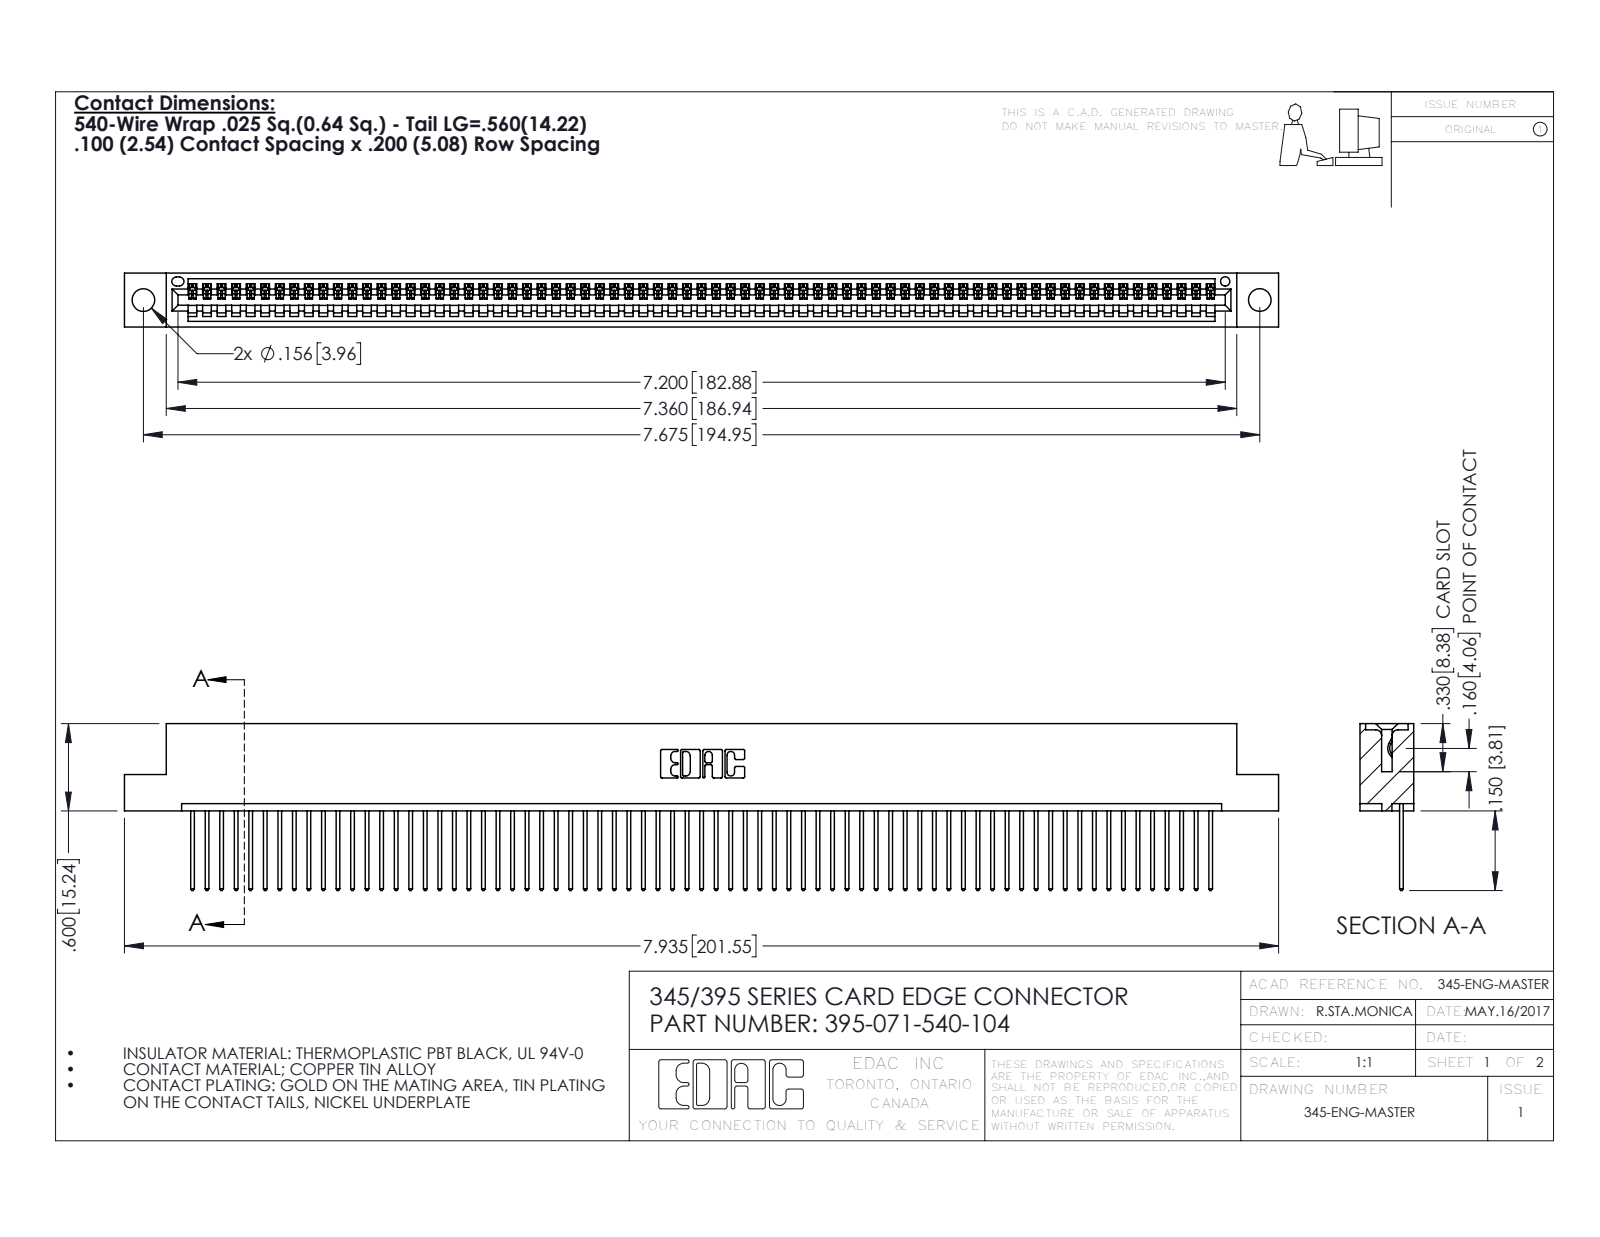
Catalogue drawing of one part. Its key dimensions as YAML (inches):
part_name: "345-292-001_345-293-140; 345 Part_Flush Mounting Lugs - 0.156 Dia-TH; 395-071-540-104"
step_written_by: "SolidWorks 2016 (CONFIG_CONTROL_DESIGN)"
units: inches
bodies: {solids: 72, faces: 4244, planar: 2920, cylindrical: 1324, other: 0}
overall_size: [7.935, 1.147, 0.37]
volume: 1.183
surface_area: 41.32
round_holes:
  - {diameter: 0.156, count: 2}
  - {diameter: 0.064, count: 1}
partial_cylinders:
  - {radius: 0.006, count: 142}
  - {radius: 0.01, count: 142}
  - {radius: 0.01, count: 22}
  - {radius: 0.007, count: 6}
  - {radius: 0.031, count: 6}
  - {radius: 0.026, count: 3}
  - {radius: 0.031, count: 2}
  - {radius: 0.04, count: 2}
face_to_face_distances: [0.072, 0.298, 0.37, 0.098, 0.272, 0.025, 0.2, 0.225, 0.149, 0.072]
hole_center_spacings: [0.27, 7.439, 7.675]
